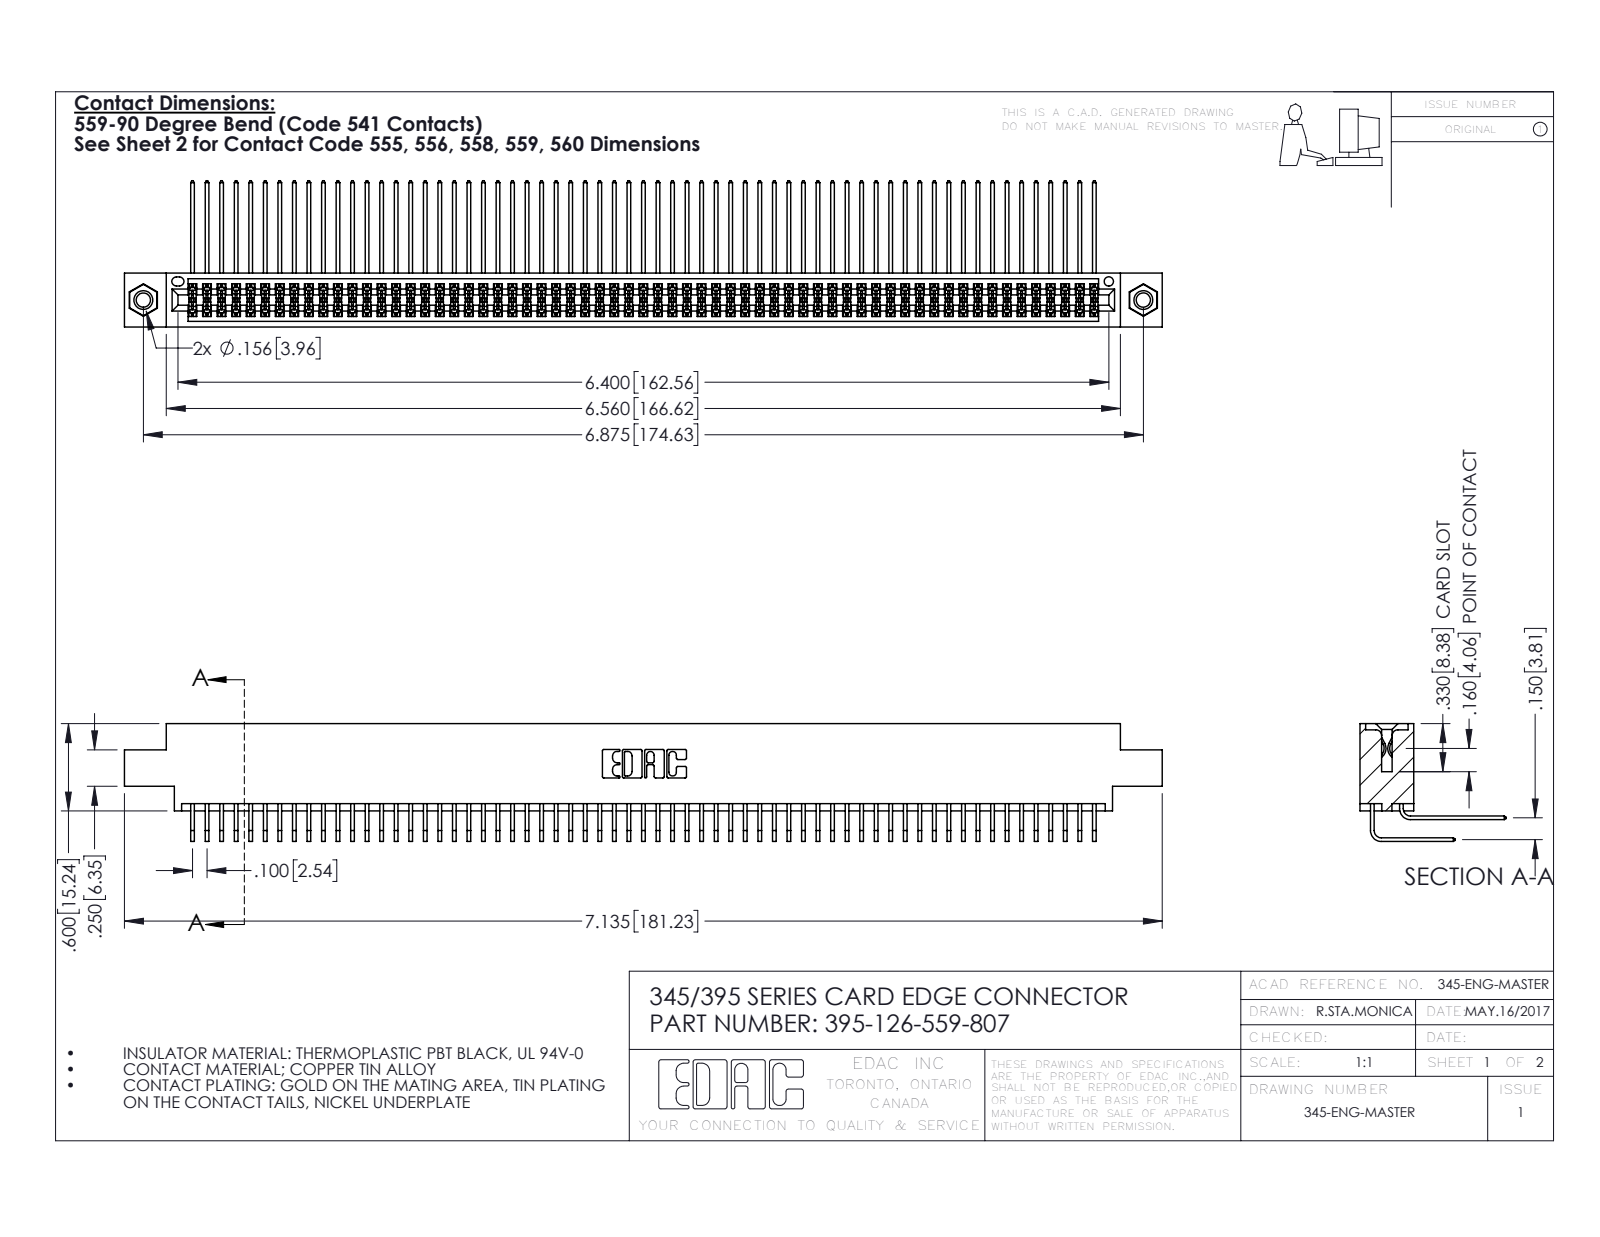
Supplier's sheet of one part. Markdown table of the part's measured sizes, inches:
| quantity | value |
| --- | --- |
| part name | 345-292-001_558 559 Tail - 1; 345-250-001_345-250-005-103; 395-126-559-807; 345-292-001_559 Tail - 2 (+1 more) |
| STEP written by | SolidWorks 2016 (CONFIG_CONTROL_DESIGN) |
| units | inches |
| bodies | 129 solids, 6742 faces (4526 planar, 2200 cylindrical, 16 other) |
| overall size | 7.135 × 1.005 × 0.809 |
| volume | 1.123 in³ |
| surface area | 48.35 in² |
| round holes (diameter × count) | 0.098 × 2, 0.125 × 2, 0.156 × 2, 0.064 × 1 |
| round bosses / shafts (diameter × count) | 0.155 × 2 |
| partial cylindrical surfaces (radius × count) | 0.006 × 190, 0.01 × 22, 0.007 × 6, 0.031 × 6, 0.026 × 3, 0.014 × 2, 0.019 × 2, 0.022 × 2 |
| main face-to-face distances | 0.072, 0.298, 0.2, 0.37, 0.098, 0.272, 0.025, 0.225, 0.175, 0.15 |
| hole center spacings | 0.27, 6.639, 6.875 |
